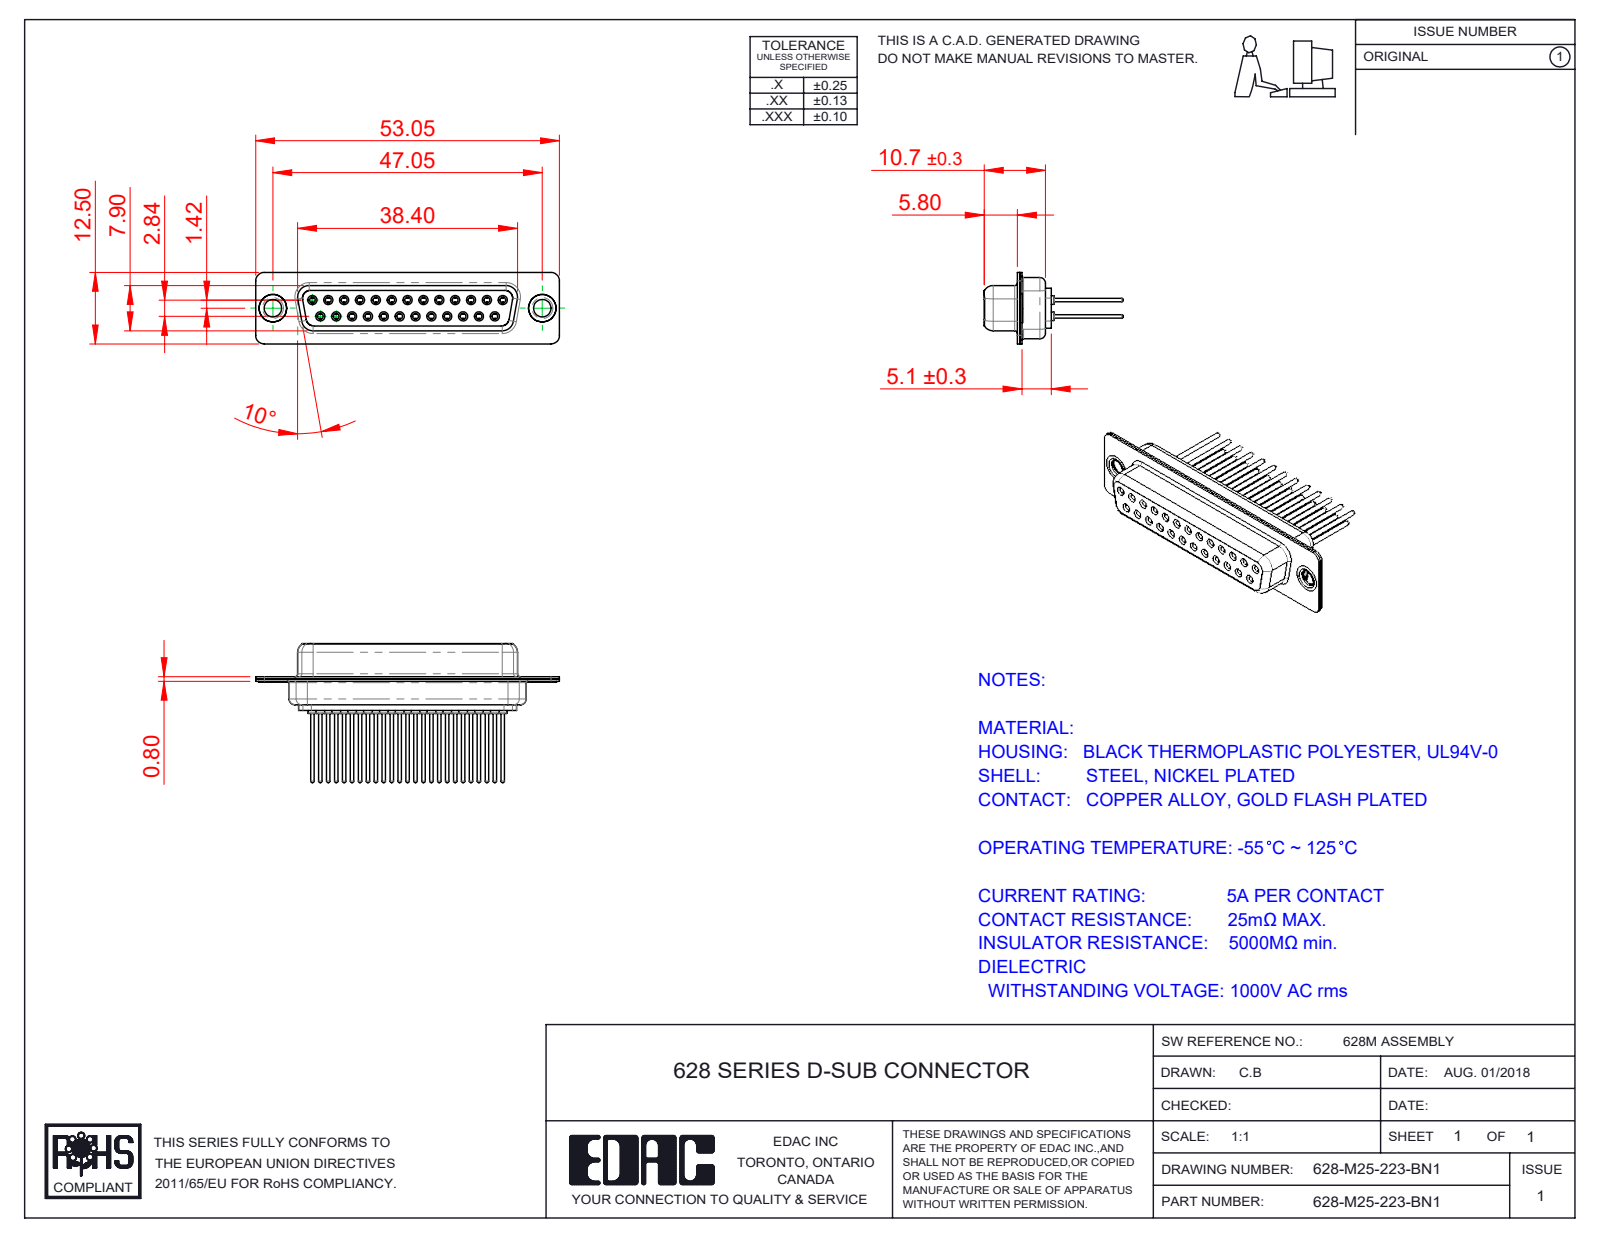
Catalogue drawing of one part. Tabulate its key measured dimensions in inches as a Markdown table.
| quantity | value |
| --- | --- |
| part name | 628M Contact Row 1_23; 628M Contact Row 2_23; 628M Housing_25 Contacts; 628-M25-223-BN1 (+3 more) |
| STEP written by | SolidWorks 2020 (CONFIG_CONTROL_DESIGN) |
| units | inches |
| bodies | 30 solids, 1628 faces (442 planar, 596 cylindrical, 590 other) |
| overall size | 2.089 × 0.956 × 0.492 |
| volume | 0.226 in³ |
| surface area | 14.44 in² |
| round holes (diameter × count) | 0.039 × 25, 0.043 × 25, 0.067 × 25, 0.071 × 25, 0.079 × 25, 0.12 × 2, 0.157 × 2, 0.189 × 2 |
| round bosses / shafts (diameter × count) | 0.087 × 25, 0.063 × 25, 0.059 × 25, 0.024 × 25, 0.197 × 2, 0.193 × 2, 0.14 × 2 |
| partial cylindrical surfaces (radius × count) | 0.059 × 16, 0.079 × 12, 0.053 × 8, 0.063 × 8, 0.01 × 4, 0.02 × 4, 0.024 × 4, 0.026 × 4 |
| main face-to-face distances | 0.016, 0.055, 0.018, 0.333, 0.35, 0.244, 0.071, 0.278, 0.039, 0.073 |
| hole center spacings | 0.124, 0.109, 0.218, 0.327, 0.436, 0.545, 0.198, 0.295 |
